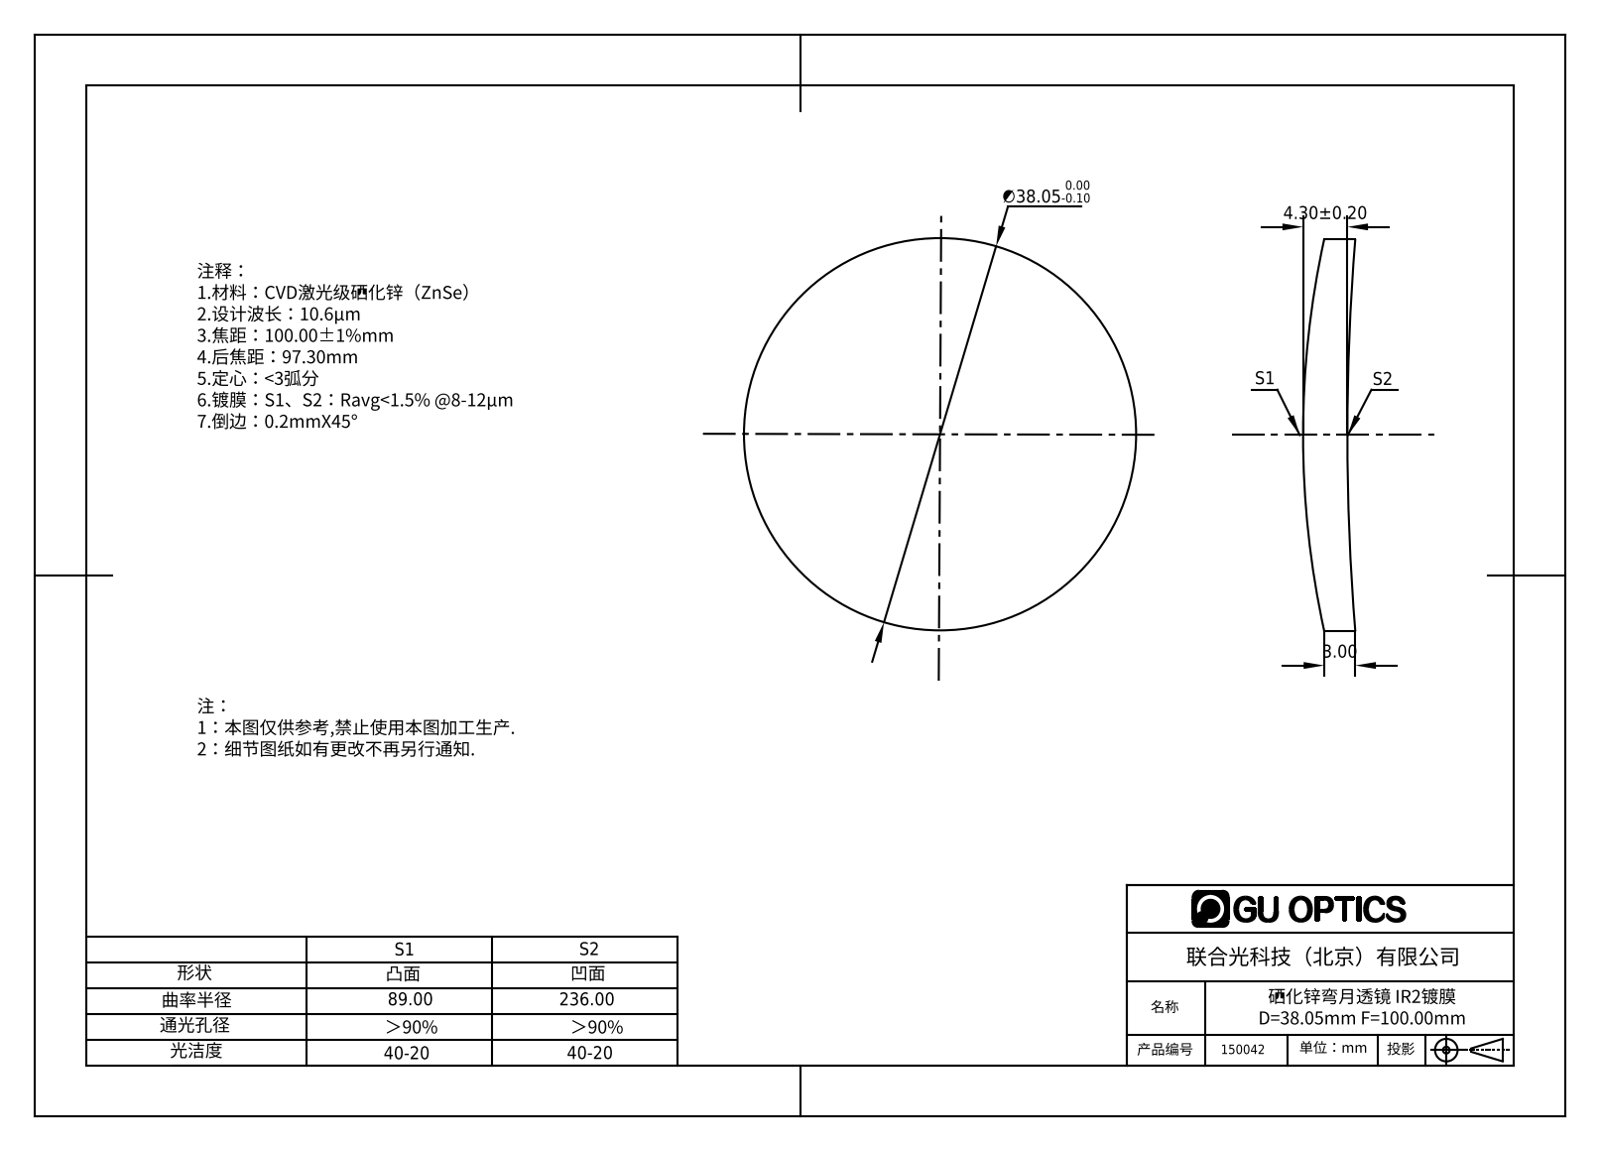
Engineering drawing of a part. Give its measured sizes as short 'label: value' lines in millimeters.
name: 150018
written by: SolidWorks 2016 (AUTOMOTIVE_DESIGN)
unit: mm
bodies: 1 solid, 6 faces (0 planar, 2 cylindrical, 4 other)
size: 38.05 × 38.05 × 5.07
volume: 4 161 mm³; area: 2 649 mm²
bosses: 1× ⌀38.05
